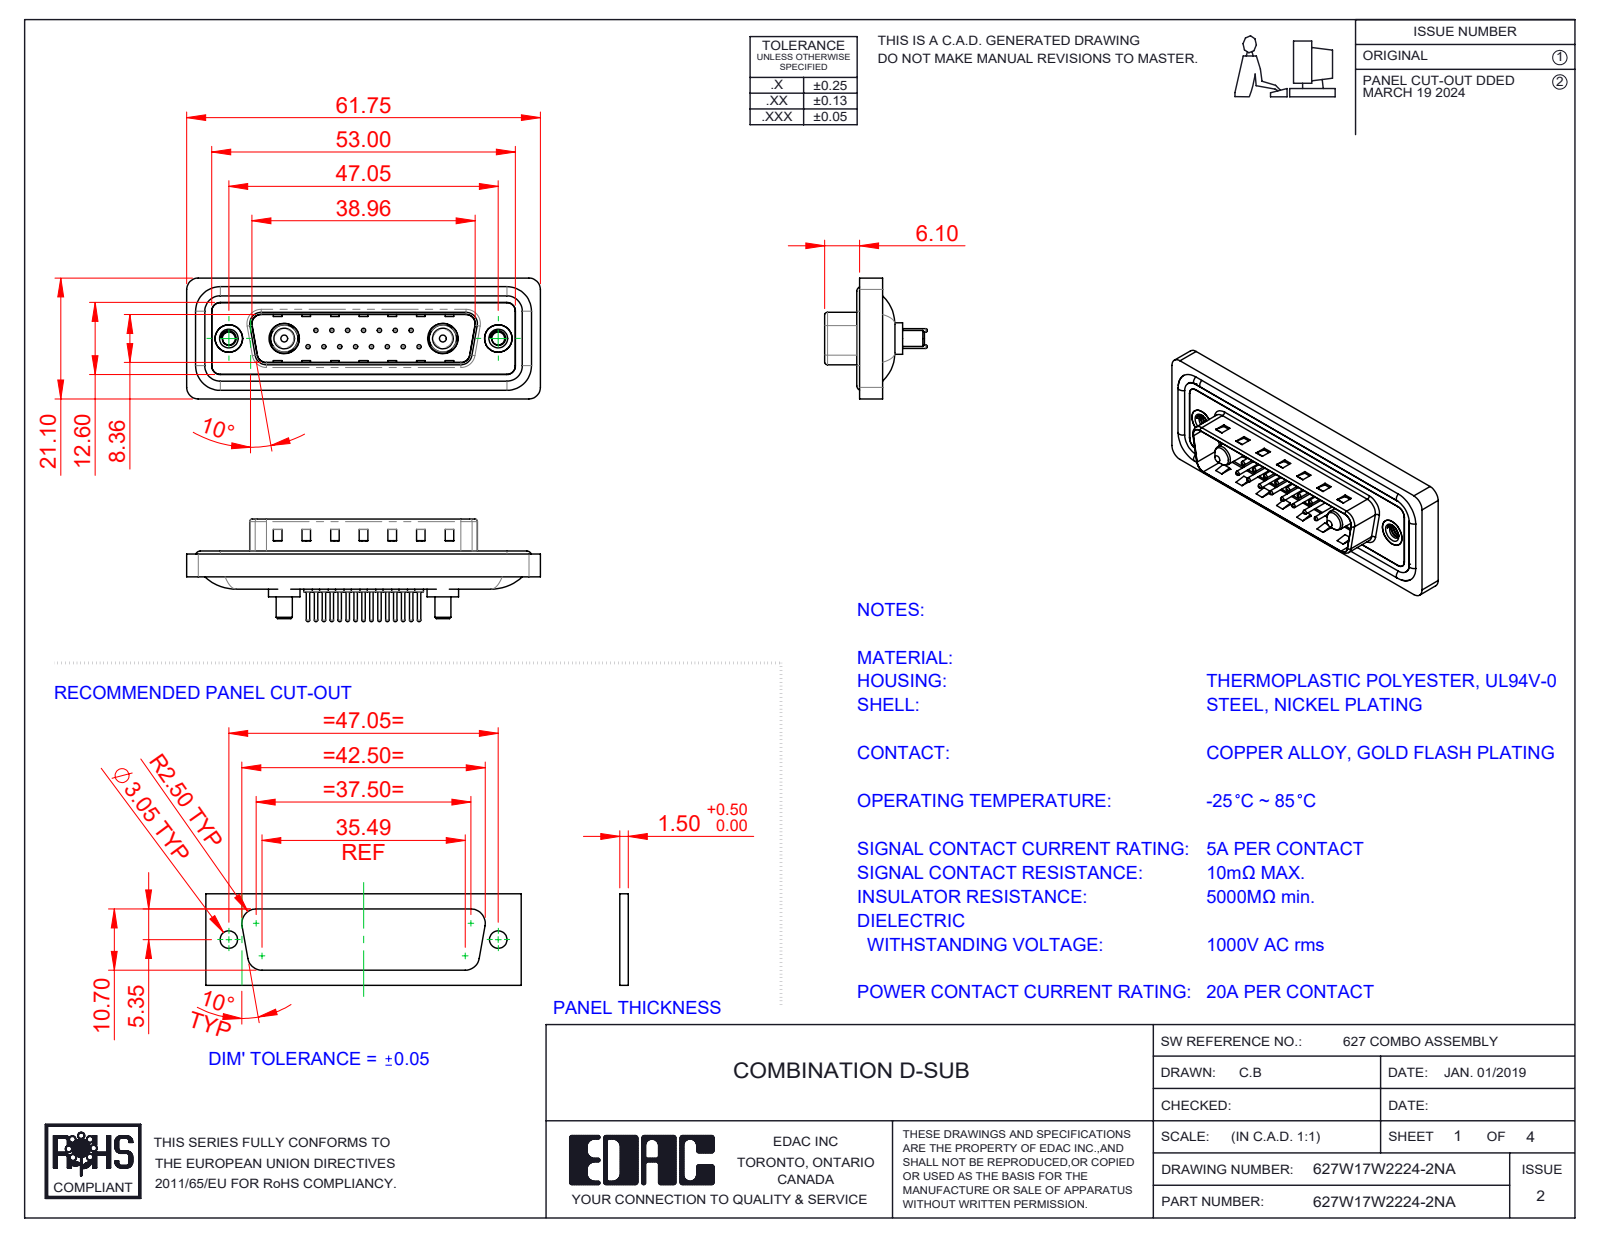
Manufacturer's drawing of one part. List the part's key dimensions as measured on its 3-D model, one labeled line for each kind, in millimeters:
Part name (STEP PRODUCT): 627Combo Shell Rear_25 Contacts; 627Combo Housing_17W2; 627Combo Contact Row 1_24; 627Combo Shell Front_25 Contacts (+5 more)
STEP written by: SolidWorks 2023 (CONFIG_CONTROL_DESIGN)
Units: millimetres
Bodies: 26 solids, 1114 faces (334 planar, 438 cylindrical, 342 other)
Overall size (bounding box): 61.75 × 21.1 × 17.9
Volume: 7 268 mm³ · Surface area: 11 912 mm²
Round holes (diameter × count): ⌀0.75 ×15, ⌀1.6 ×15, ⌀2 ×15, ⌀2.26 ×2, ⌀4 ×2, ⌀4.8 ×2, ⌀4.85 ×2, ⌀5 ×2, ⌀5.3 ×2
Round bosses / shafts (diameter × count): ⌀1.5 ×15, ⌀0.6 ×15, ⌀1.6 ×4, ⌀5.5 ×2, ⌀5.2 ×2, ⌀4.9 ×2, ⌀4.75 ×2, ⌀3.75 ×2
Partial cylindrical surfaces — rounded edges, fillets, slot ends (radius × count): R1.5 ×22, R2 ×18, R0.5 ×8, R1.6 ×8, R0.25 ×4, R0.6 ×4, R0.65 ×4, R0.9 ×4
Main face-to-face distances: 0.4, 1.5, 1.1, 1.6, 0.5, 3.1, 2.9, 0.82, 9.58, 4.1
Hole centre spacings: 3.16, 2.77, 5.54, 8.31, 5.04, 7.49, 11.08, 5.03
